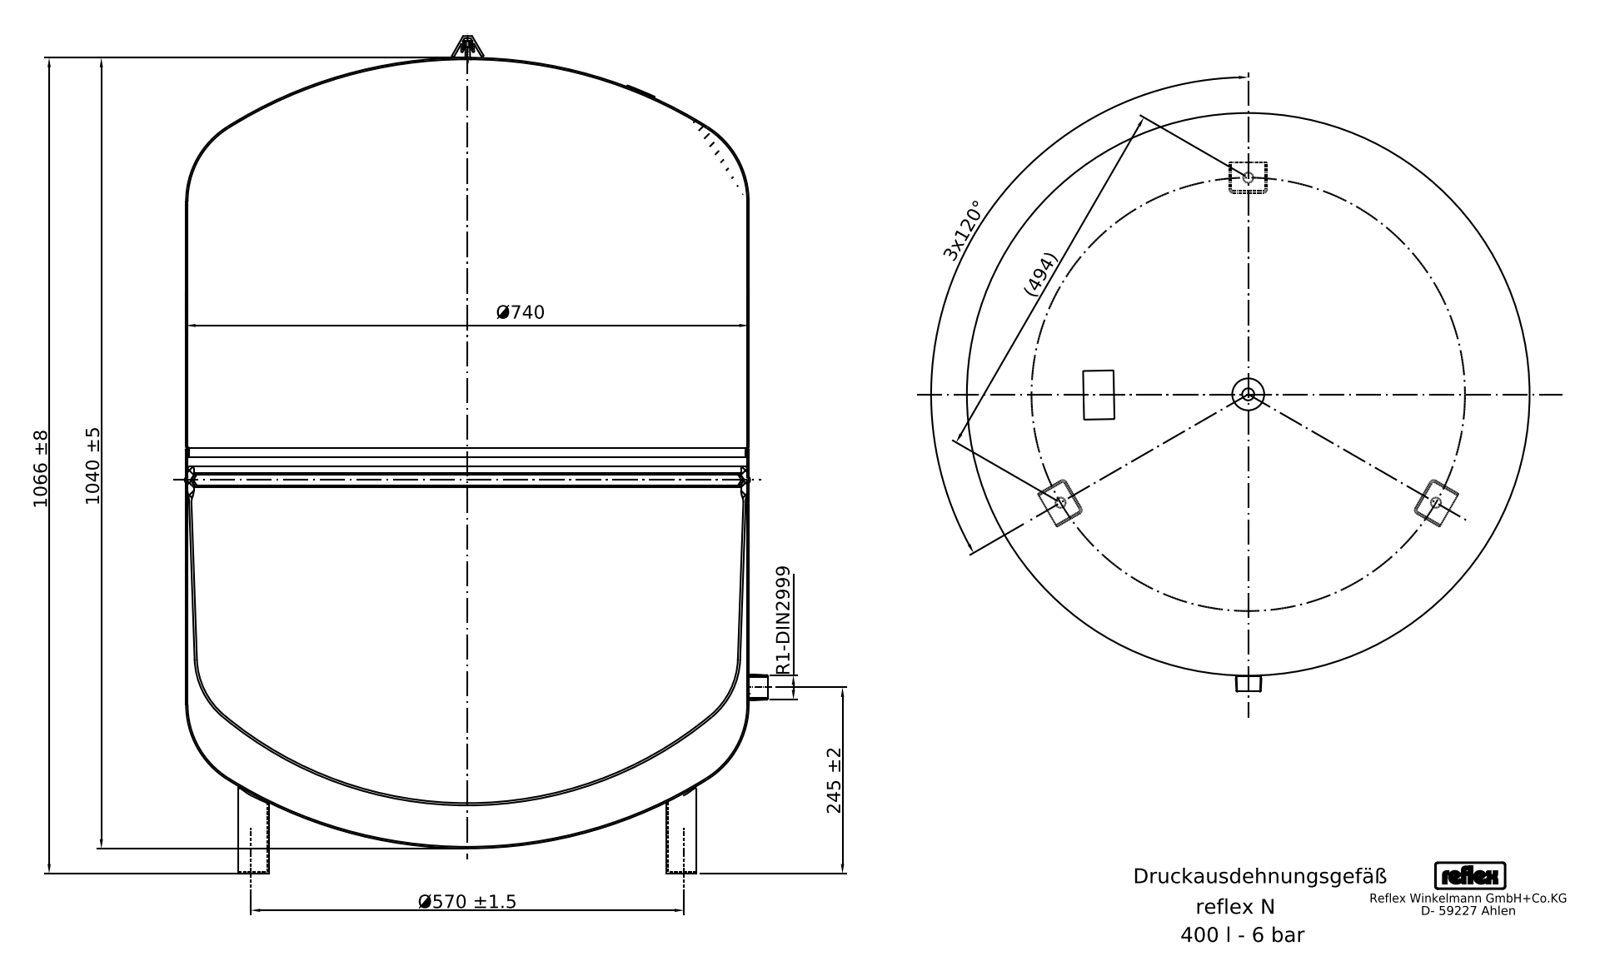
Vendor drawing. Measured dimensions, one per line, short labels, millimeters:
written by: Mechanical Desktop 2008 (CONFIG_CONTROL_DESIGN)
unit: mm
bodies: 16 solids, 250 faces (100 planar, 93 cylindrical, 57 other)
size: 1087.25 × 770.45 × 750.9
volume: 391 700 000 mm³; area: 4 593 000 mm²
holes: 3× ⌀13.4, 1× ⌀8.46, 1× ⌀25.7
bosses: 1× ⌀740, 1× ⌀33.7, 1× ⌀10.26, 1× ⌀5.4, 1× ⌀3.6
rounds: 15× R1, 15× R2.5, 15× R5, 4× R3.94, 3× R1.57, 2× R2.69, 2× R4.72, 2× R6.49
face distances: 662, 2.5, 47.5, 45, 50, 331, 217, 548, 879, 2
hole spacings: 285, 493.64
